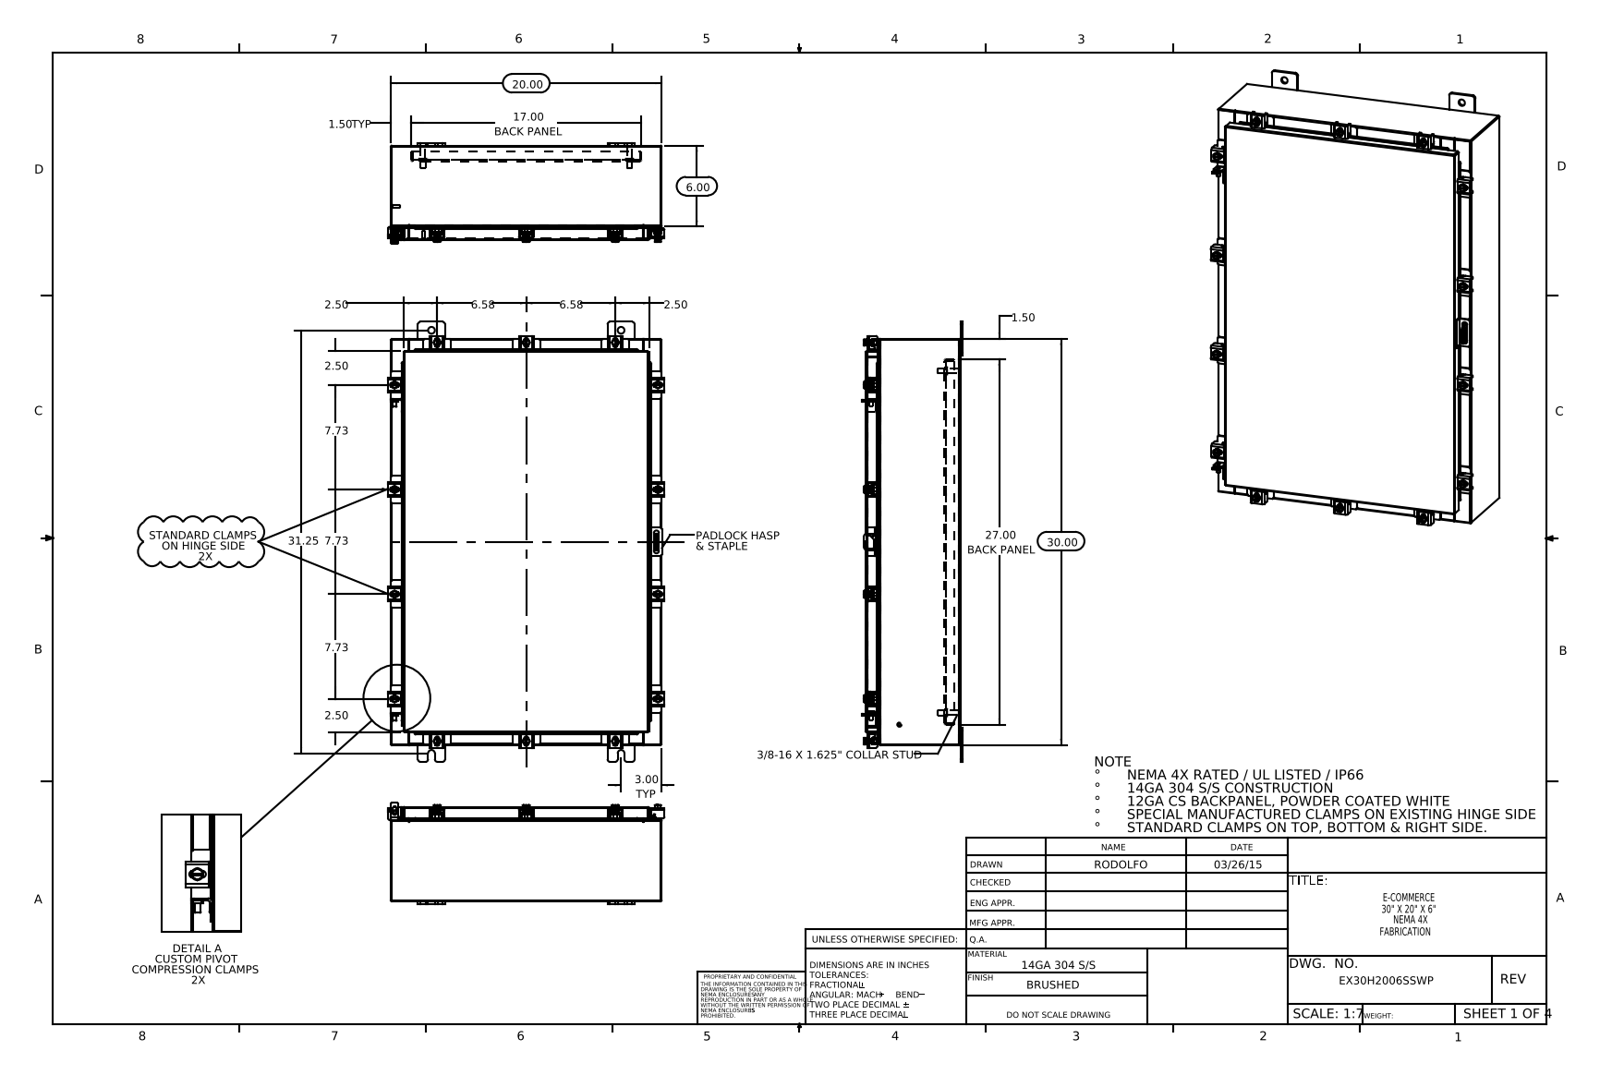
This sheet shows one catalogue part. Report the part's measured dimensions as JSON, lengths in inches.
{"part_name": "EX30H2006SSWP Clamp Assembly; Quarter-20 CD Stud; EX30H2006SSWP Top; Special Clamp Assembly (+8 more)", "step_written_by": "SolidWorks 2014 (CONFIG_CONTROL_DESIGN)", "units": "inches", "bodies": {"solids": 91, "faces": 2272, "planar": 1211, "cylindrical": 885, "other": 176}, "overall_size": [32.5, 20.421, 7.453], "volume_in3": 214, "surface_area_in2": 5301, "round_holes": [[0.213, 14], [0.26, 14], [0.5, 8], [0.125, 1], [0.25, 1]], "round_bosses_or_shafts": [[0.5, 14], [0.25, 14], [0.399, 12], [0.625, 4], [0.375, 4], [0.33, 4], [0.315, 2], [0.236, 2]], "partial_cylinders_radius": [[0.06, 62], [0.141, 28], [0.013, 26], [0.12, 26], [0.19, 24], [0.088, 22], [0.09, 20], [0.05, 19]], "face_to_face_distances": [0.075, 6.9, 6.975, 6.826, 0.104, 1, 1.075, 5.826, 5.9, 1.179], "hole_center_spacings": [2.347, 4.44, 16.602, 19.451, 24.31, 26.507, 27.371, 29.793]}
